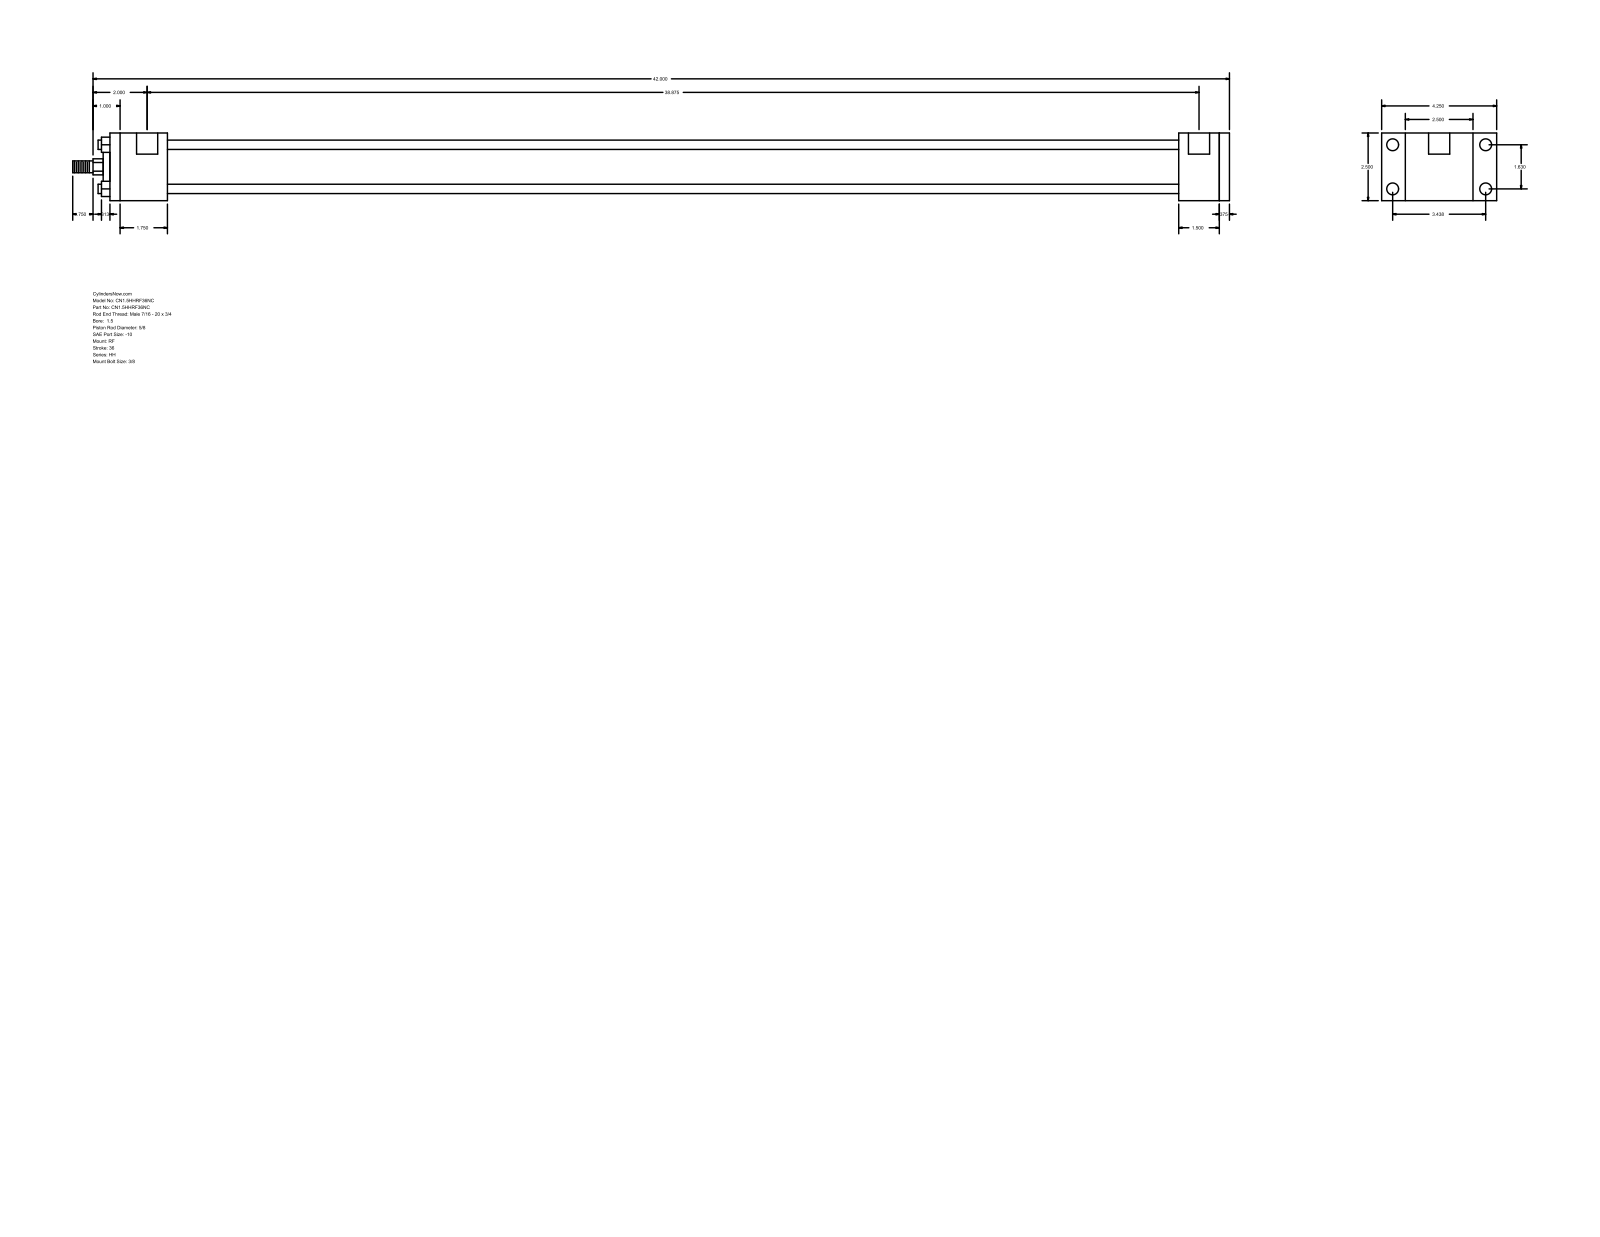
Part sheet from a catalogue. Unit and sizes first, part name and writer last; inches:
Units: inches
Overall size (bounding box): 42.75 × 4.25 × 2.5
Round holes (diameter × count): ⌀0.219 ×4, ⌀0.438 ×4, ⌀0.781 ×2
Round bosses / shafts (diameter × count): ⌀0.345 ×4, ⌀1.75 ×1, ⌀1.125 ×1, ⌀0.625 ×1, ⌀0.437 ×1
Partial cylindrical surfaces — rounded edges, fillets, slot ends (radius × count): R0.297 ×1
Main face-to-face distances: 2.5, 41.375, 41, 0.375, 1.875, 2.125, 39.5, 37.375, 38.875, 39.25
Hole centre spacings: 0.063, 1.63, 3.438, 3.805, 38.937, 39, 38.875
Bodies: 0 solids, 92 faces (64 planar, 28 cylindrical, 0 other)
Part name (STEP PRODUCT): HH_RF__0150_0.625
STEP written by: GSSL Pune (CONFIG_CONTROL_DESIGN)
